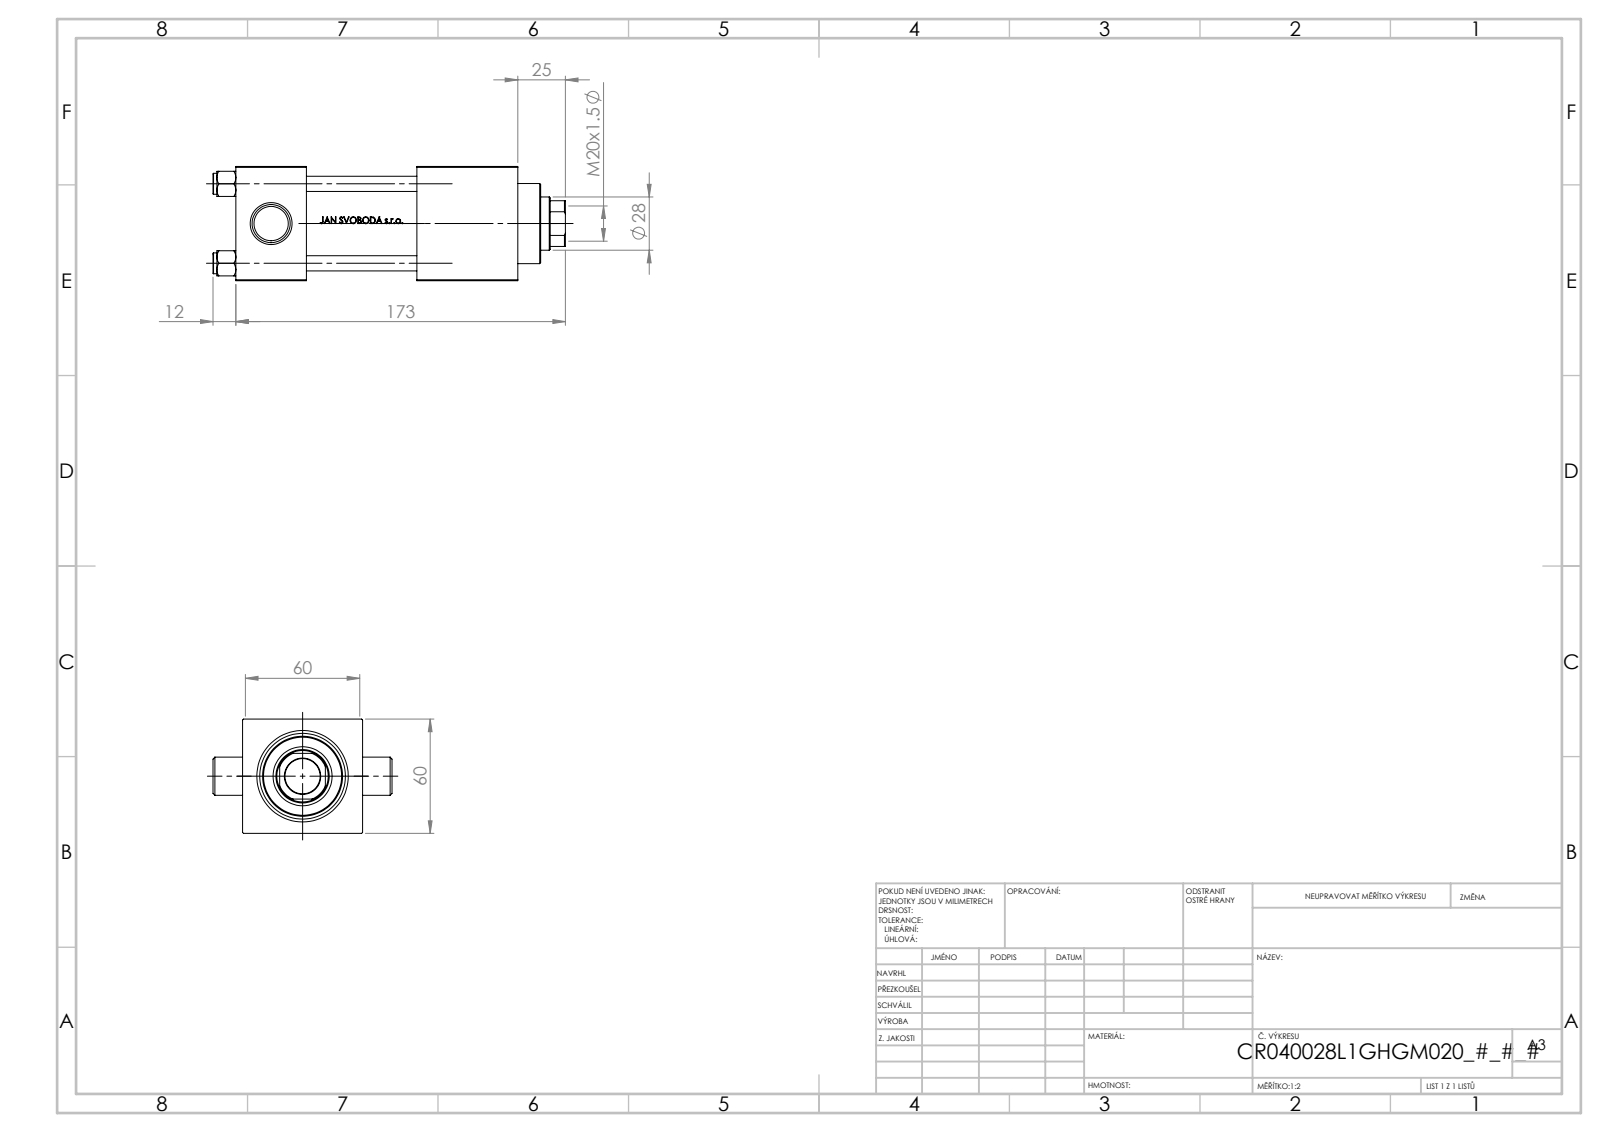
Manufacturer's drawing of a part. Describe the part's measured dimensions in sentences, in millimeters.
The part is named "V215CR_VCP_L; NUT_M5_L; V215_VC_A; V215CR_L_TYCINKA (+1 more)". Its 3-D file was written by "SolidWorks 2019 (CONFIG_CONTROL_DESIGN)". It is 11 solids with 1063 faces: 427 planar, 114 cylindrical and 522 other. Overall it measures 185 by 94 by 60 millimeters. Its volume is 452 954 cubic millimeters and its surface area 109 700 square millimeters. Round holes: 4 of diameter 8, 2 of diameter 2.5, 1 of diameter 7, 1 of diameter 18.5, 1 of diameter 28, 1 of diameter 31, 1 of diameter 40, 1 of diameter 45. Round bosses or shafts: 4 of diameter 11, 1 of diameter 46, 1 of diameter 42, 1 of diameter 20. Partial cylindrical surfaces (rounded edges, fillets, slot ends): 1 of radius 13.5. The main face-to-face distances are 60, 37, 1.5, 61.5, 63, 95, 58, 148, 111, 53. The hole center spacings are 20.85, 29.49, 41.7, 46.53, 20.75, 58.97, 41.5.
